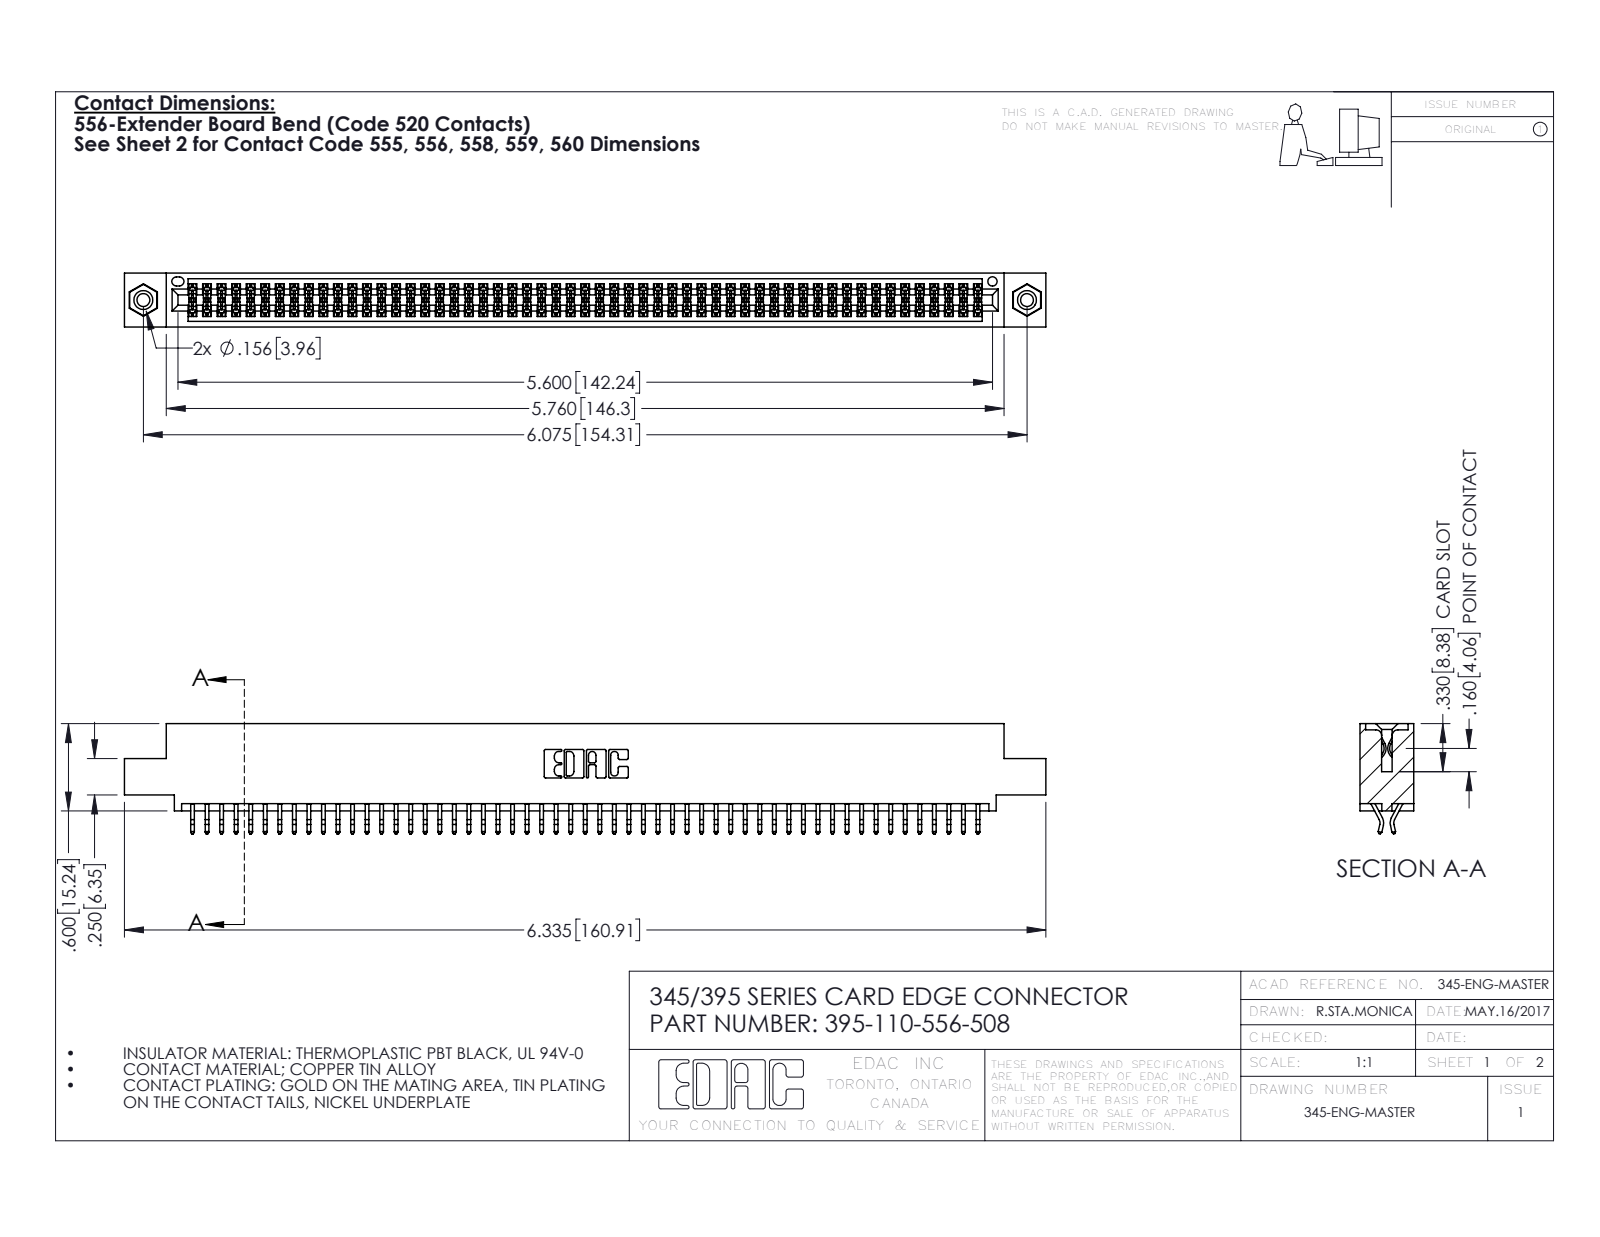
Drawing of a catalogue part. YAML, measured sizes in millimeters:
part_name: "345 Part_0.110 Offset - 0.156 Dia-TI; 345-292-001_556 Tail; 395-110-556-508; 345-250-001_345-250-003-102"
step_written_by: "SolidWorks 2016 (CONFIG_CONTROL_DESIGN)"
units: millimeters
bodies: {solids: 113, faces: 6350, planar: 4186, cylindrical: 2148, other: 16}
overall_size: [160.9, 19.2, 9.4]
volume: 15700
surface_area: 23420
round_holes:
  - {diameter: 2.3, count: 2}
  - {diameter: 3.2, count: 2}
  - {diameter: 4, count: 2}
  - {diameter: 1.6, count: 1}
round_bosses_or_shafts:
  - {diameter: 3.9, count: 2}
partial_cylinders:
  - {radius: 0.2, count: 165}
  - {radius: 0.3, count: 22}
  - {radius: 0.2, count: 6}
  - {radius: 0.8, count: 6}
  - {radius: 0.7, count: 3}
  - {radius: 0.3, count: 2}
  - {radius: 0.4, count: 2}
  - {radius: 0.5, count: 2}
face_to_face_distances: [1.8, 7.6, 9.4, 5.1, 0.6, 2.5, 6.9, 5.7, 4.4, 3.8]
hole_center_spacings: [6.9, 148.3, 154.3]
